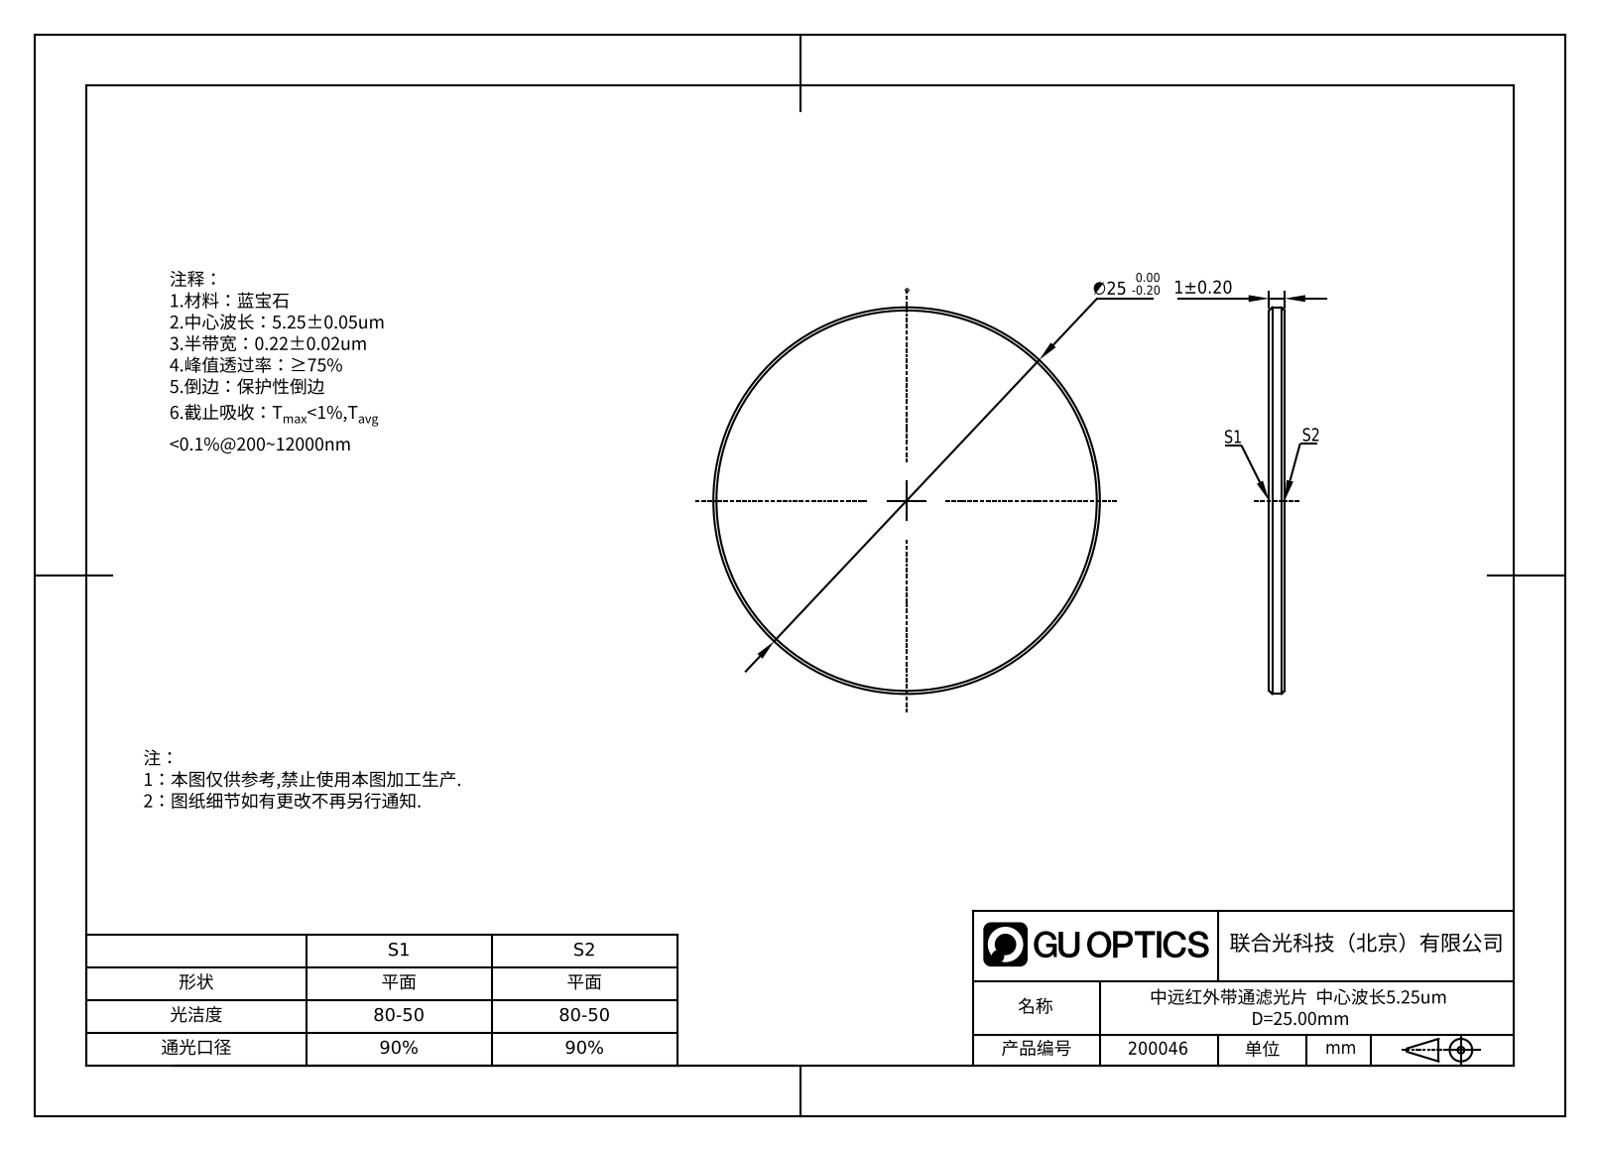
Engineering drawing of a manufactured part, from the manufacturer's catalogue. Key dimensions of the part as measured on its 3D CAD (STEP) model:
Part name (STEP PRODUCT): GNIF-220-5250-D25
STEP written by: SolidWorks 2022 (AUTOMOTIVE_DESIGN)
Units: millimetres
Bodies: 1 solid, 8 faces (2 planar, 2 cylindrical, 4 other)
Overall size (bounding box): 25 × 25 × 1
Volume: 488 mm³ · Surface area: 1 042 mm²
Round bosses / shafts (diameter × count): ⌀25 ×1
Main face-to-face distances: 1
